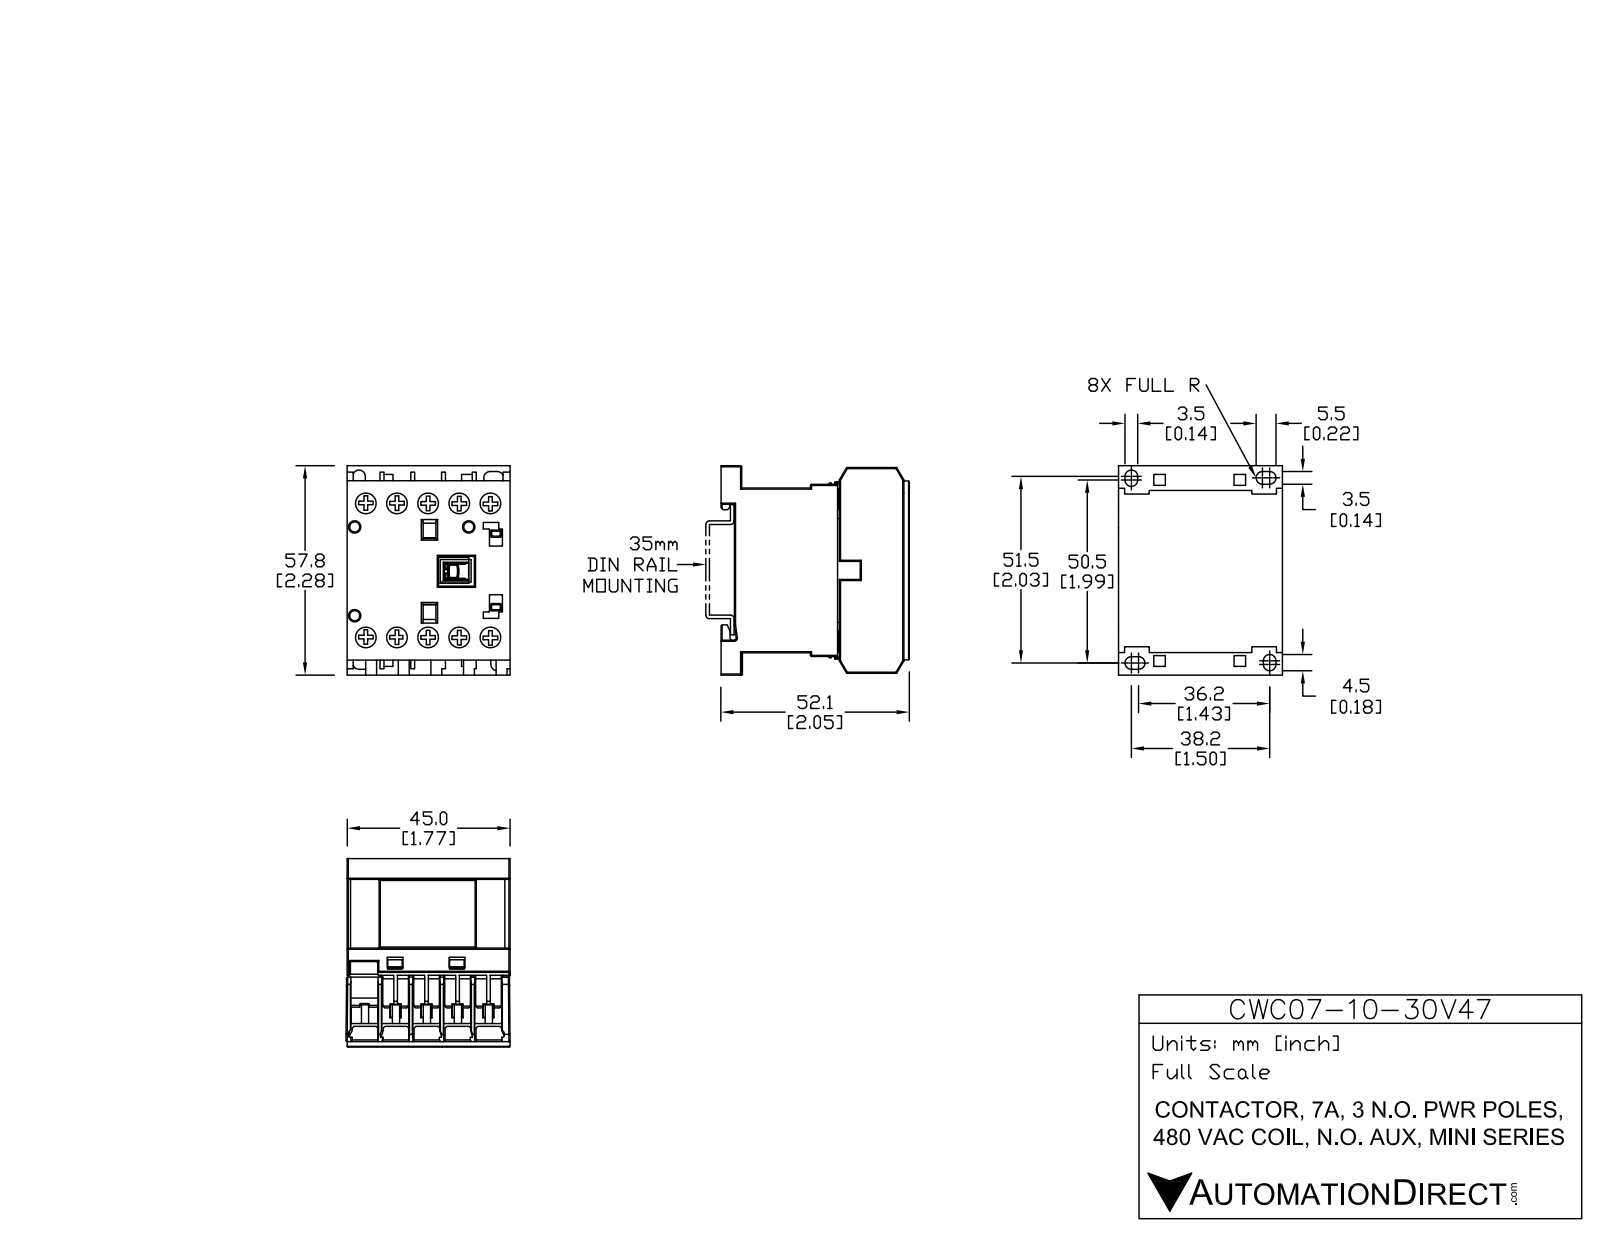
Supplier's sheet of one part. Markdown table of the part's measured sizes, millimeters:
| quantity | value |
| --- | --- |
| part name | CWC07-10-30V47 |
| STEP written by | SolidWorks 2013 (AUTOMOTIVE_DESIGN) |
| units | millimeters |
| bodies | 15 solids, 535 faces (445 planar, 90 cylindrical, 0 other) |
| overall size | 58.04 × 52.12 × 45.75 |
| volume | 97 133 mm³ |
| surface area | 30 437 mm² |
| round holes (diameter × count) | 6.2 × 10, 2.8 × 3 |
| round bosses / shafts (diameter × count) | 5.9 × 10 |
| partial cylindrical surfaces (radius × count) | 0.3 × 20, 1.72 × 6, 1.73 × 2, 0.32 × 1, 0.42 × 1, 0.55 × 1 |
| main face-to-face distances | 8.25, 45.5, 1.25, 16.5, 9.5, 5.5, 17.75, 5.13, 10.63, 7 |
| hole center spacings | 8.55, 37.94, 17.1, 40.72, 36.96, 25.65, 44.99, 6.91 |
